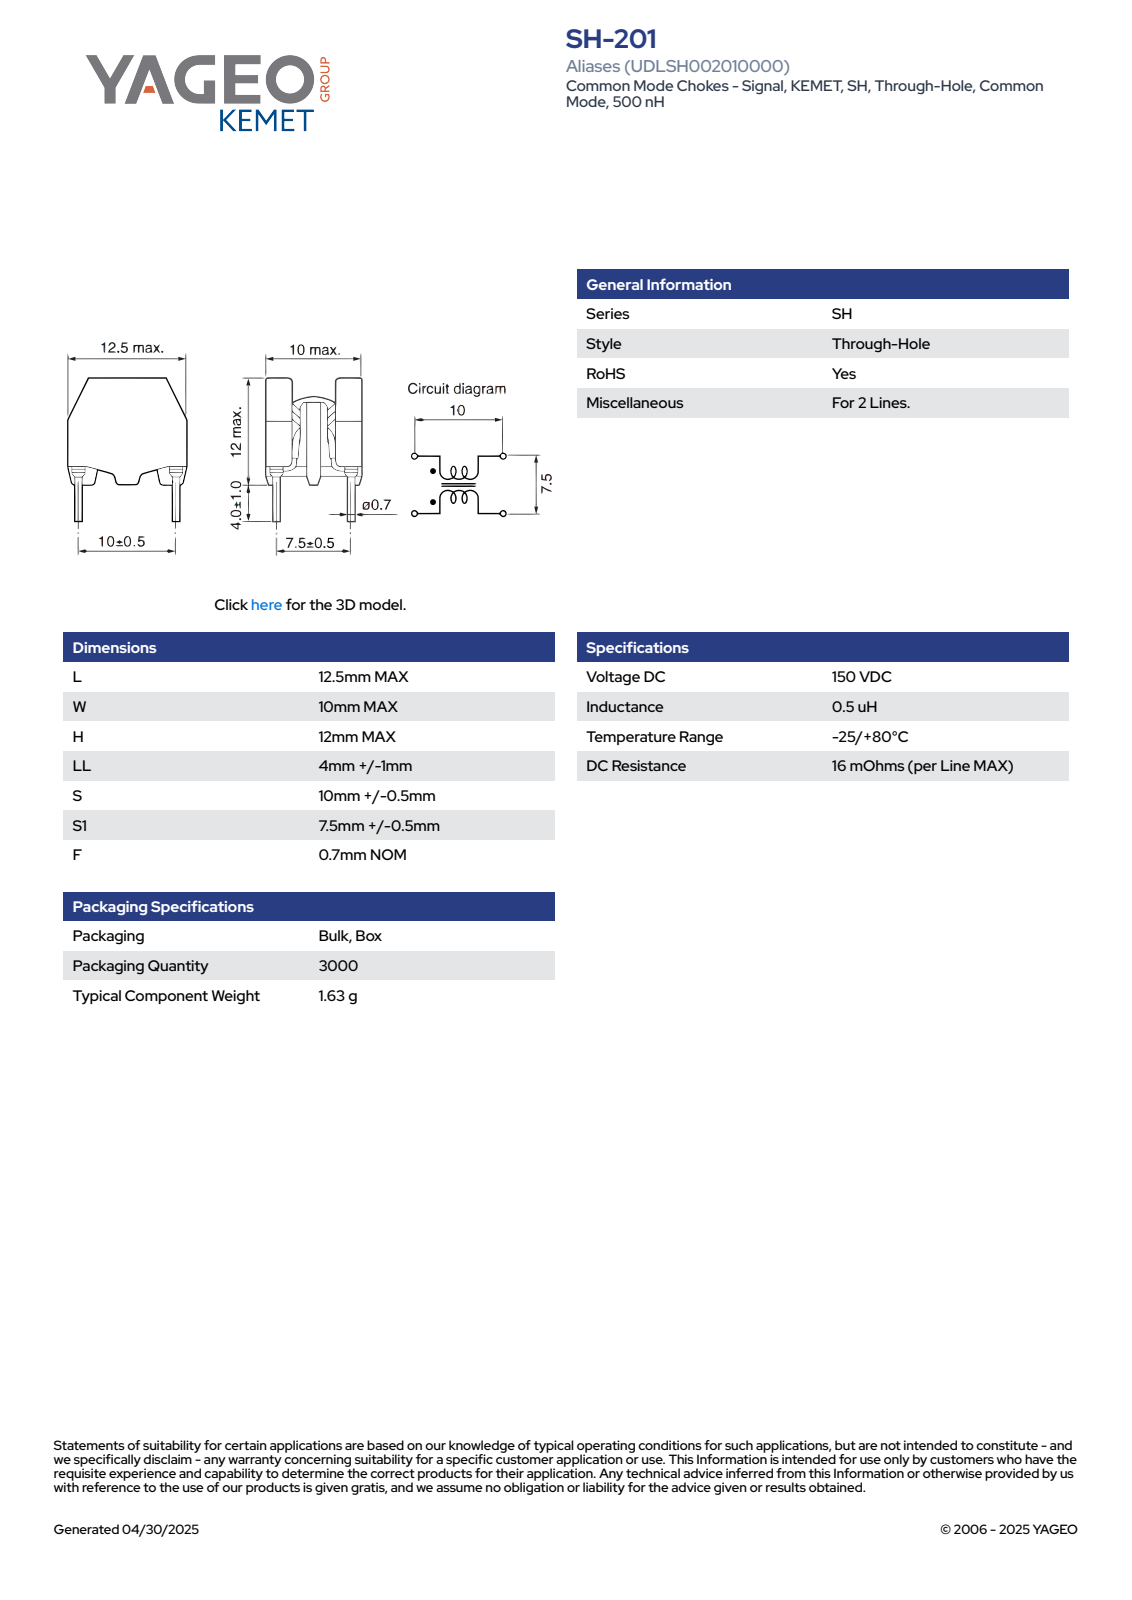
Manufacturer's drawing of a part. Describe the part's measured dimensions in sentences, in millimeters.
The part is named "IFC_DCSH1_L12.5W10H12". Its 3-D file was written by "SolidWorks 2014 (AUTOMOTIVE_DESIGN)". It is 1 solid with 208 faces: 103 planar, 89 cylindrical and 16 other. Overall it measures 17 by 12.5 by 10 millimeters. Its volume is 788 cubic millimeters and its surface area 1 170 square millimeters. Round bosses or shafts: 4 of diameter 0.9, 4 of diameter 0.7, 1 of diameter 6, 1 of diameter 5.51. Partial cylindrical surfaces (rounded edges, fillets, slot ends): 52 of radius 0.25, 1 of radius 3.05. The main face-to-face distances are 8.25, 1.75, 4.2, 5.8, 2.45, 4.05, 10, 6.5, 1.6, 1.2.
